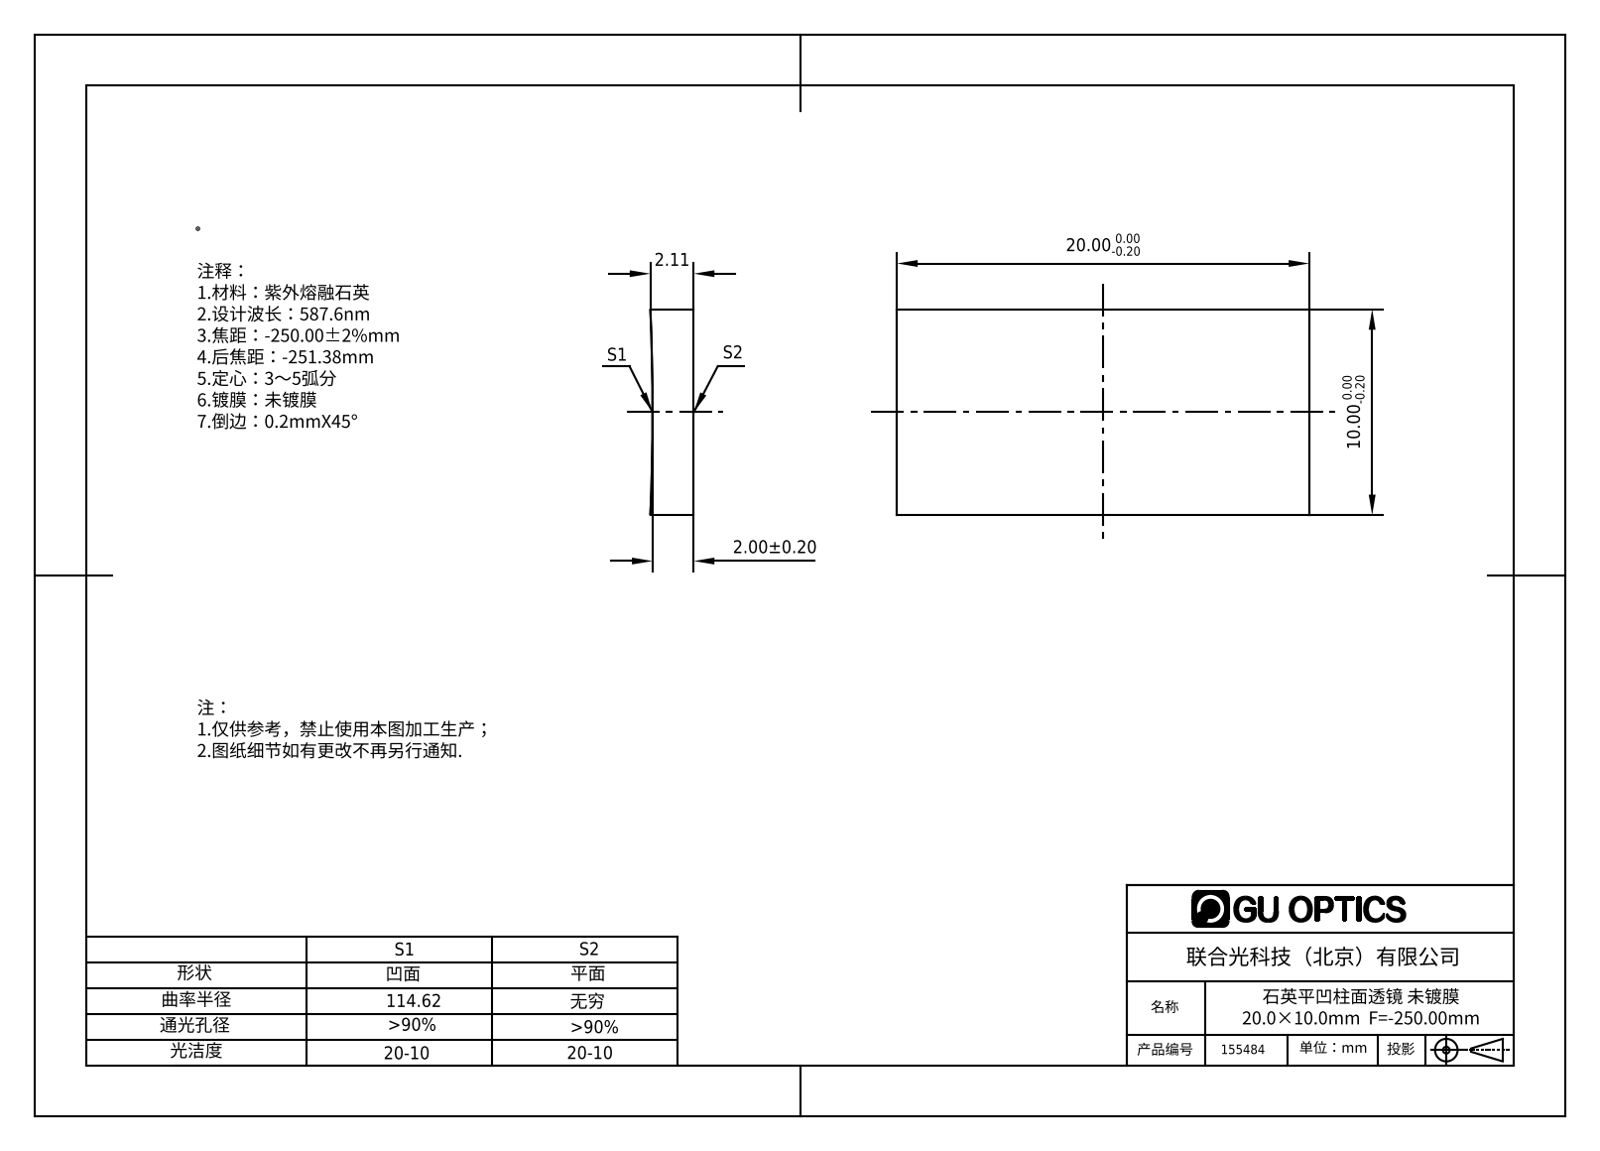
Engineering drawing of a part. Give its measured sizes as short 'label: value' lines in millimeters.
name: 155484
written by: SolidWorks 2016 (AUTOMOTIVE_DESIGN)
unit: mm
bodies: 1 solid, 6 faces (5 planar, 1 cylindrical, 0 other)
size: 20 × 10 × 2.11
volume: 407 mm³; area: 525 mm²
rounds: 1× R114.62
face distances: 10, 20
